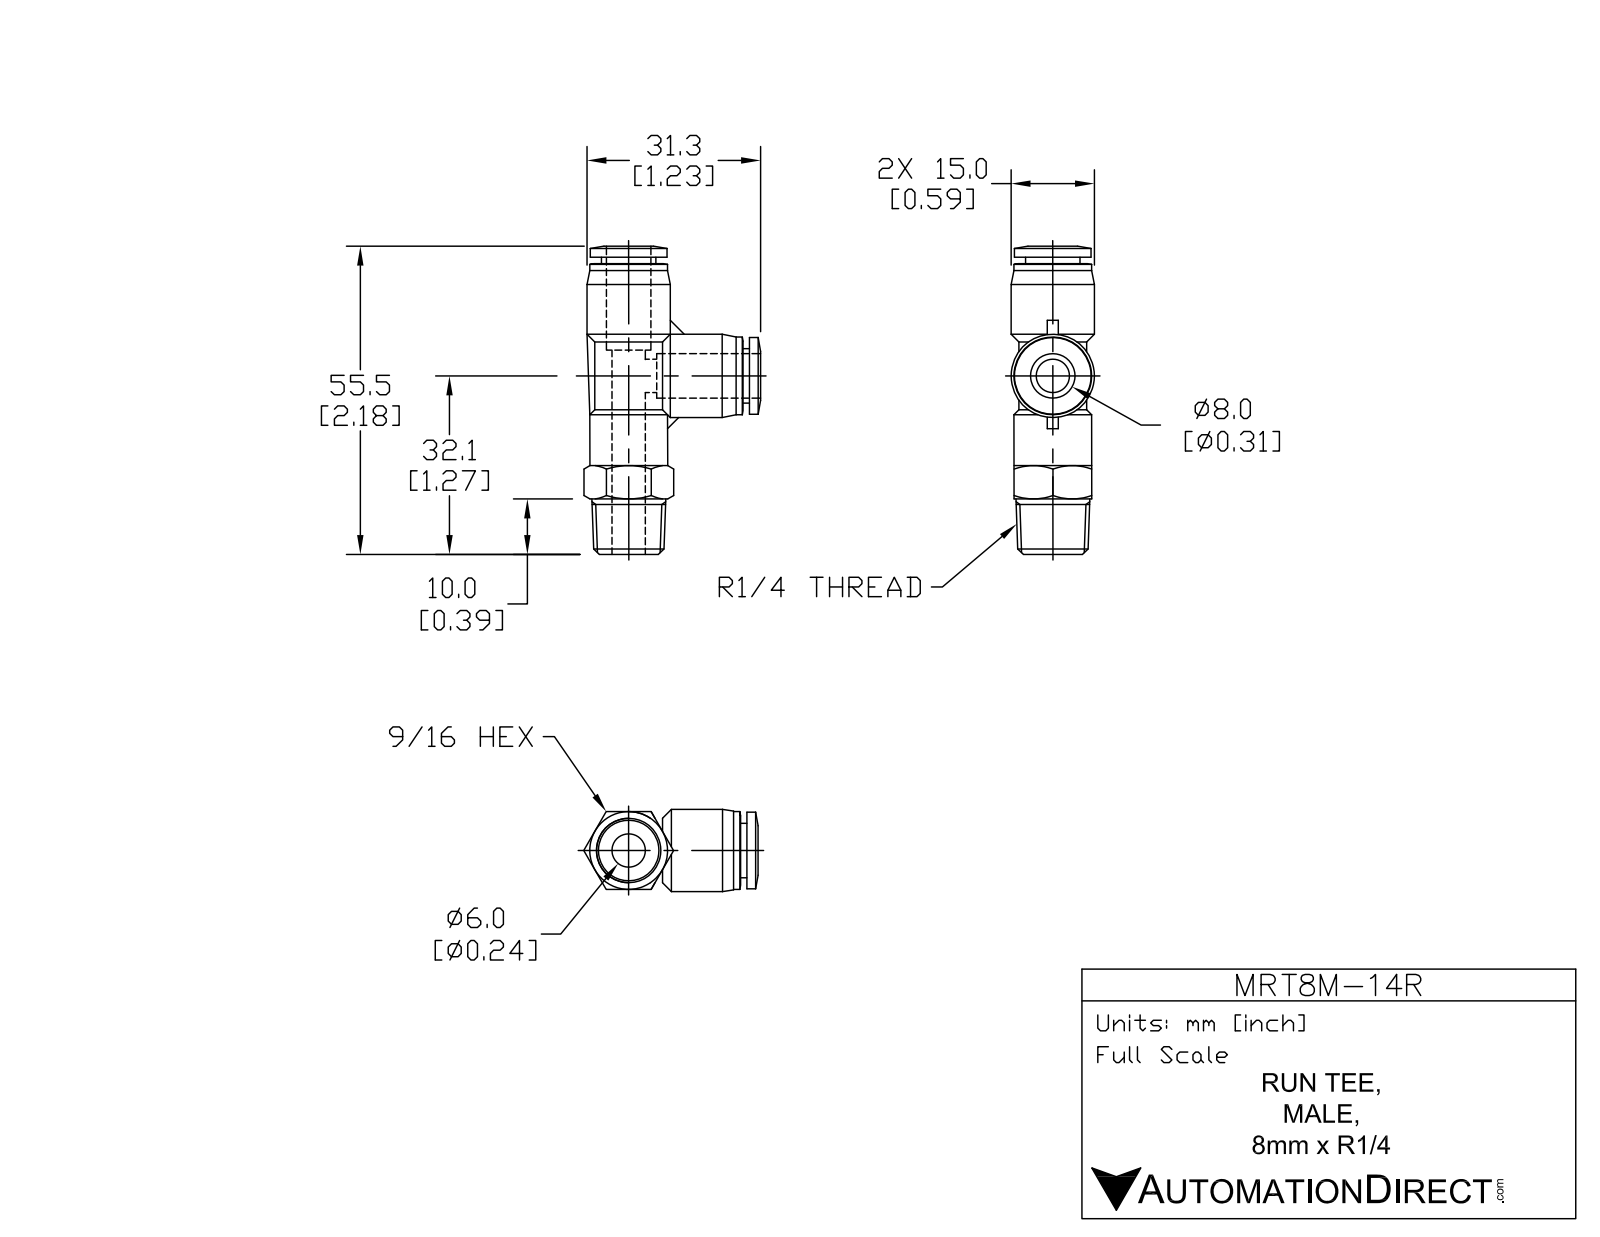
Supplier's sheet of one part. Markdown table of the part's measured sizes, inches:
| quantity | value |
| --- | --- |
| part name | MRT8M-14R |
| STEP written by | SolidWorks 2015 (AUTOMOTIVE_DESIGN) |
| units | inches |
| bodies | 1 solid, 101 faces (24 planar, 34 cylindrical, 43 other) |
| overall size | 2.169 × 1.238 × 0.591 |
| volume | 0.475 in³ |
| surface area | 8.425 in² |
| round holes (diameter × count) | 0.236 × 2, 0.327 × 2 |
| round bosses / shafts (diameter × count) | 0.591 × 2, 0.551 × 2, 0.543 × 2, 0.48 × 2, 0.386 × 2 |
| main face-to-face distances | 0.551, 0.045, 2.091, 0.596, 0.642, 2.045, 0.236, 0.315, 0.079, 1.449 |
